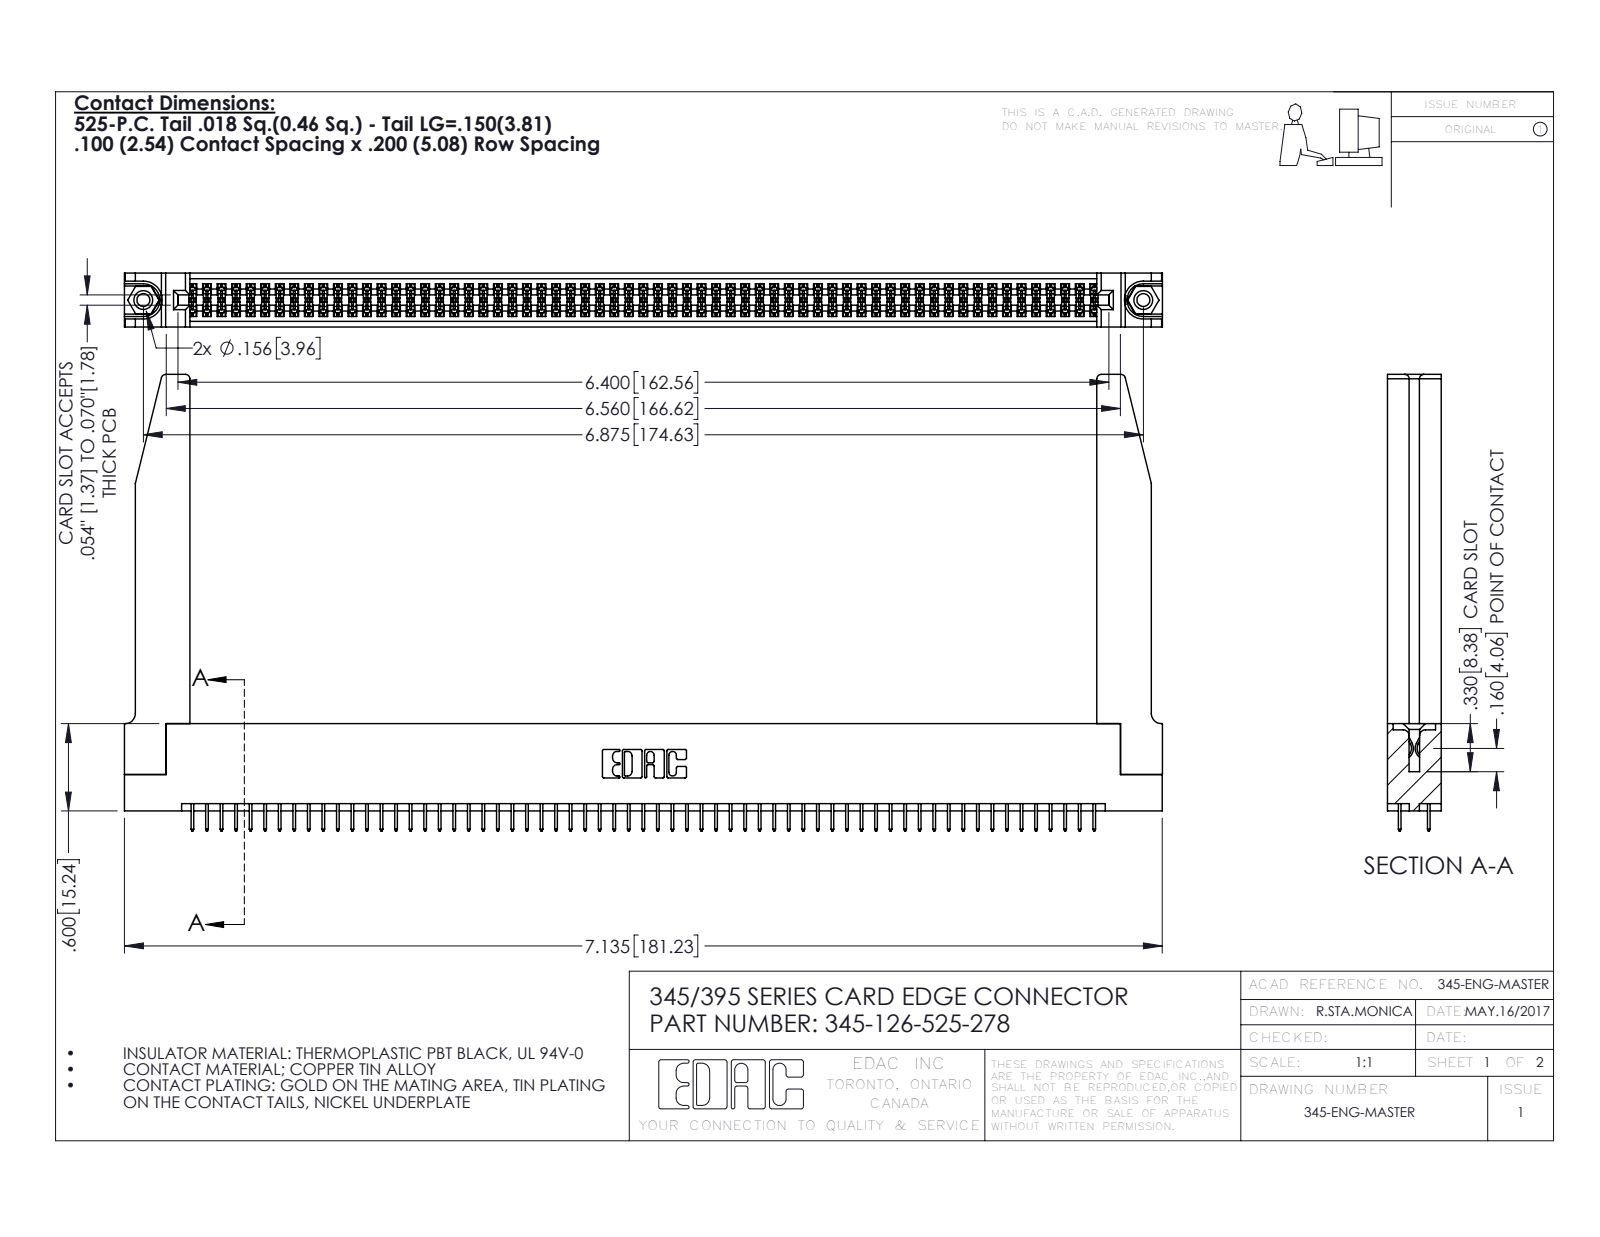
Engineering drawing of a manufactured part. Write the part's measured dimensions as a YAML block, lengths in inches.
part_name: "345-220-078_345-220-078; 345-126-525-278; 345-250-001_345-250-001-102; 345 Part_Flush Mounting Lugs - 0.156 Dia-TH (+1 more)"
step_written_by: "SolidWorks 2020 (CONFIG_CONTROL_DESIGN)"
units: inches
bodies: {solids: 131, faces: 7164, planar: 5136, cylindrical: 1976, other: 52}
overall_size: [7.136, 3.137, 0.37]
volume: 1.548
surface_area: 50.57
round_holes:
  - {diameter: 0.089, count: 2}
  - {diameter: 0.125, count: 2}
  - {diameter: 0.156, count: 2}
  - {diameter: 0.064, count: 1}
round_bosses_or_shafts:
  - {diameter: 0.155, count: 2}
partial_cylinders:
  - {radius: 0.006, count: 252}
  - {radius: 0.01, count: 22}
  - {radius: 0.03, count: 8}
  - {radius: 0.007, count: 6}
  - {radius: 0.031, count: 6}
  - {radius: 0.026, count: 3}
  - {radius: 0.014, count: 2}
  - {radius: 0.019, count: 2}
face_to_face_distances: [0.072, 0.37, 0.298, 0.2, 0.098, 0.272, 0.025, 0.225, 0.072, 0.175]
hole_center_spacings: [0.27, 6.639, 6.875]
